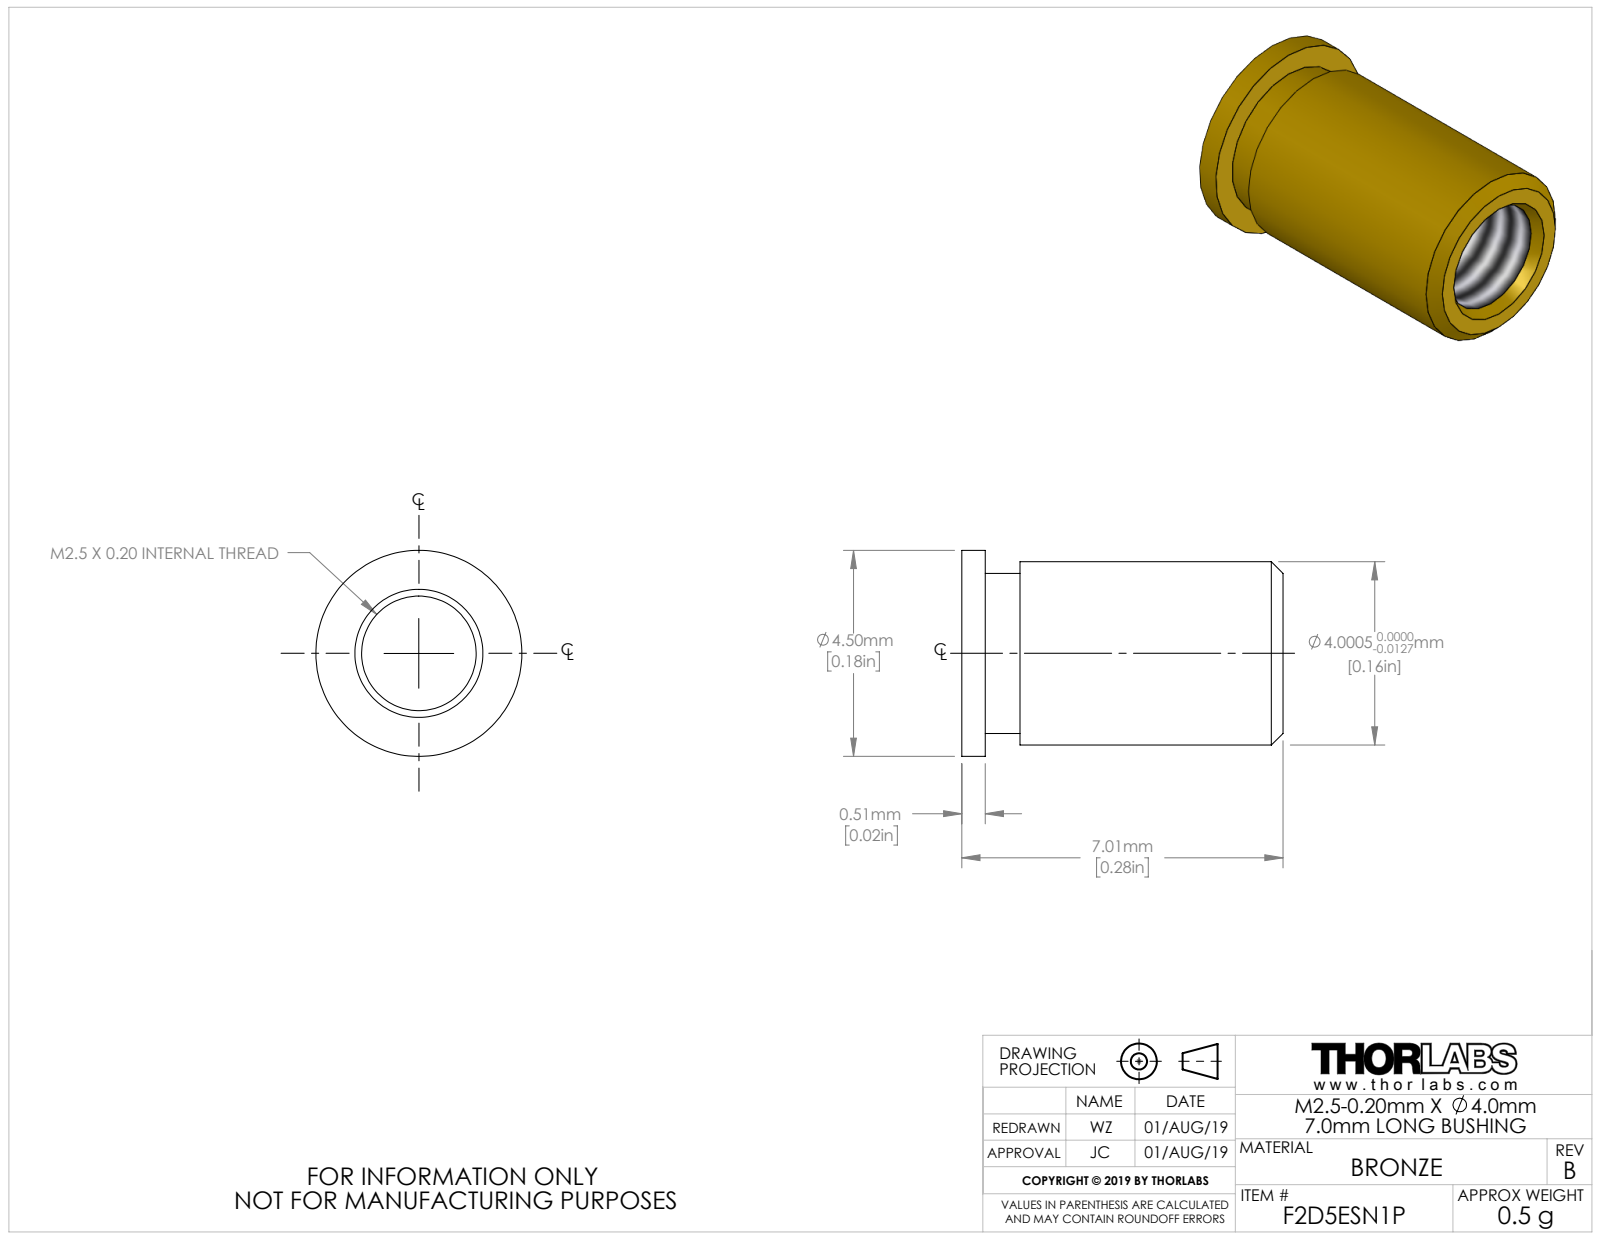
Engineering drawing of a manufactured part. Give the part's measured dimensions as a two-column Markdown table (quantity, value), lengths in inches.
| quantity | value |
| --- | --- |
| part name | 18995-E0W |
| STEP written by | SolidWorks 2007 (AUTOMOTIVE_DESIGN) |
| units | inches |
| bodies | 1 solid, 18 faces (4 planar, 8 cylindrical, 6 other) |
| overall size | 0.276 × 0.177 × 0.177 |
| volume | 0.003 in³ |
| surface area | 0.259 in² |
| round holes (diameter × count) | 0.098 × 1 |
| round bosses / shafts (diameter × count) | 0.177 × 1, 0.157 × 1, 0.137 × 1 |
| main face-to-face distances | 0.02, 0.276, 0.256, 0.05, 0.03, 0.226 |
